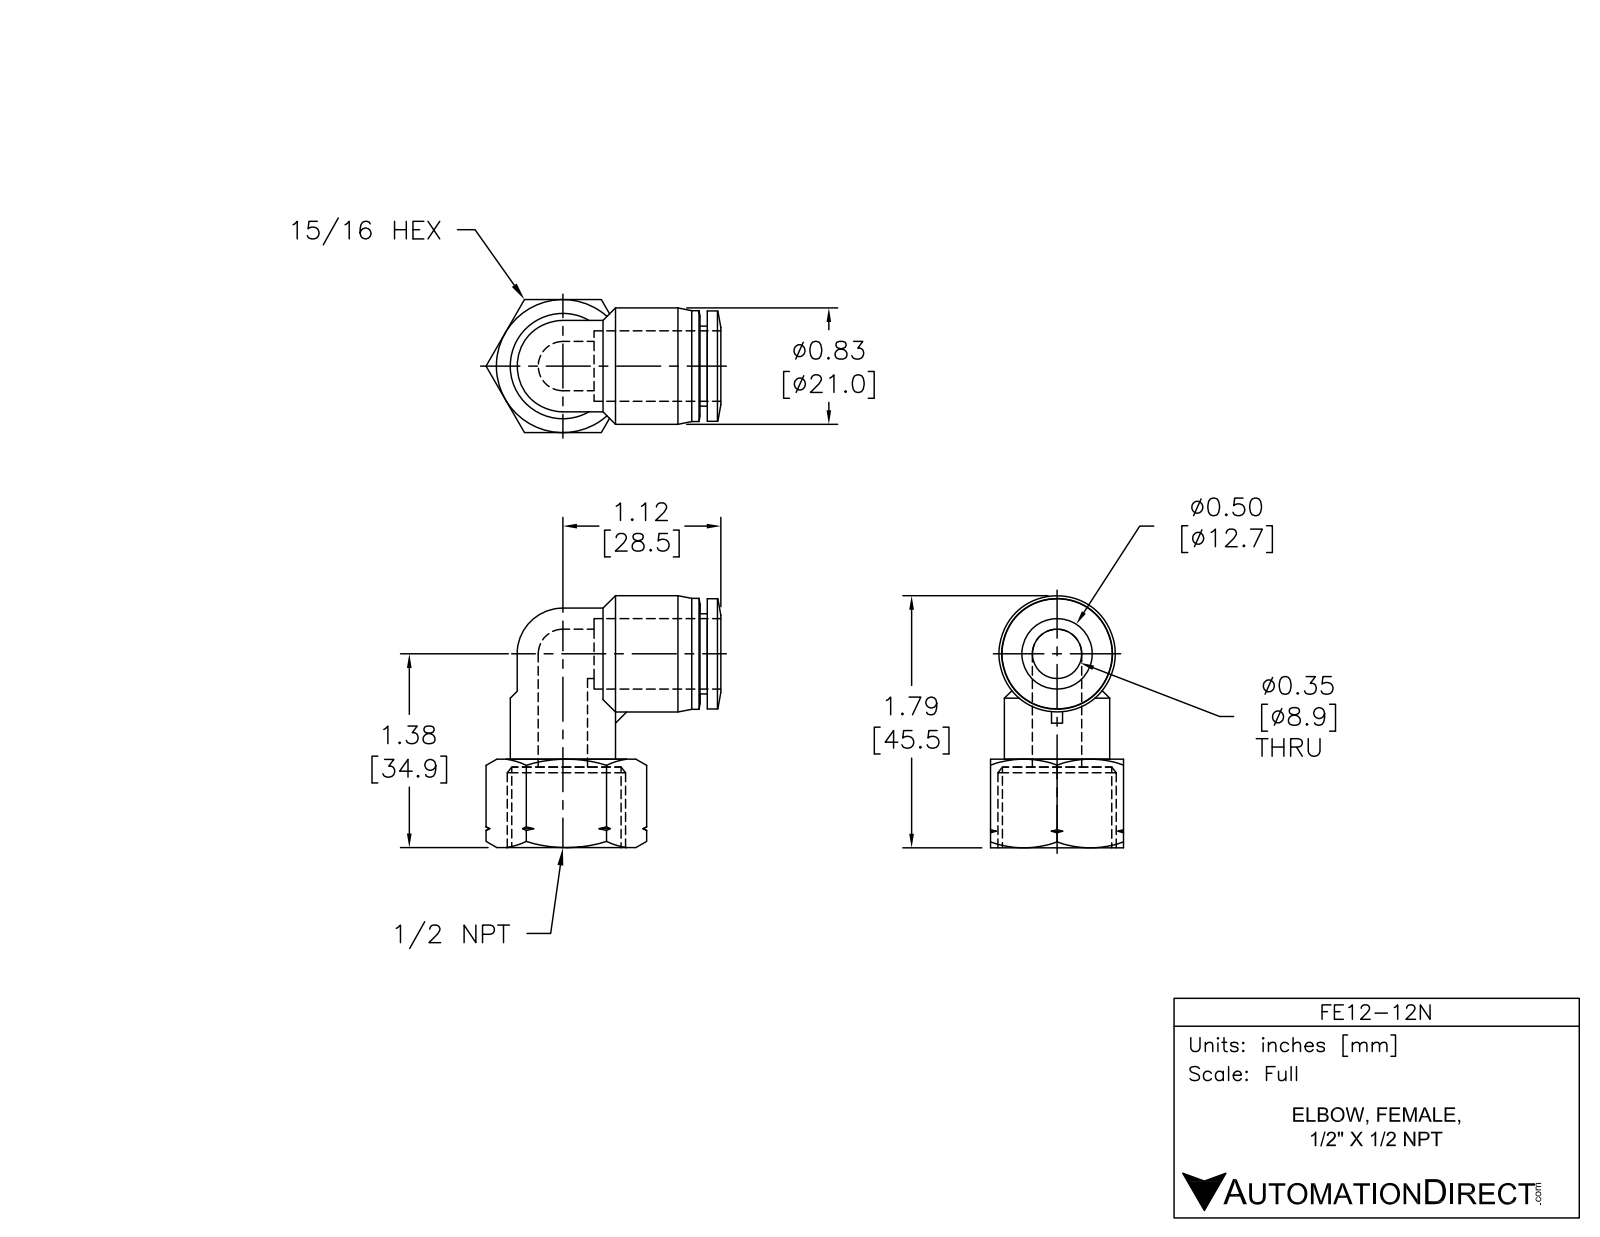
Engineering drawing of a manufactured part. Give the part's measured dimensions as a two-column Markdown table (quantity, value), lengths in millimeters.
| quantity | value |
| --- | --- |
| part name | FE12-12N |
| STEP written by | SolidWorks 2015 (AUTOMOTIVE_DESIGN) |
| units | millimeters |
| bodies | 1 solid, 84 faces (15 planar, 20 cylindrical, 49 other) |
| overall size | 45.5 × 42.1 × 24 |
| volume | 11 200 mm³ |
| surface area | 7 761 mm² |
| round holes (diameter × count) | 9 × 2, 13 × 1 |
| round bosses / shafts (diameter × count) | 16.5 × 2, 21 × 1, 20 × 1, 19.9 × 1, 19 × 1, 14.5 × 1 |
| main face-to-face distances | 24, 1.5, 14.5, 16, 1.3, 19.4, 20.7, 11, 13, 2 |
